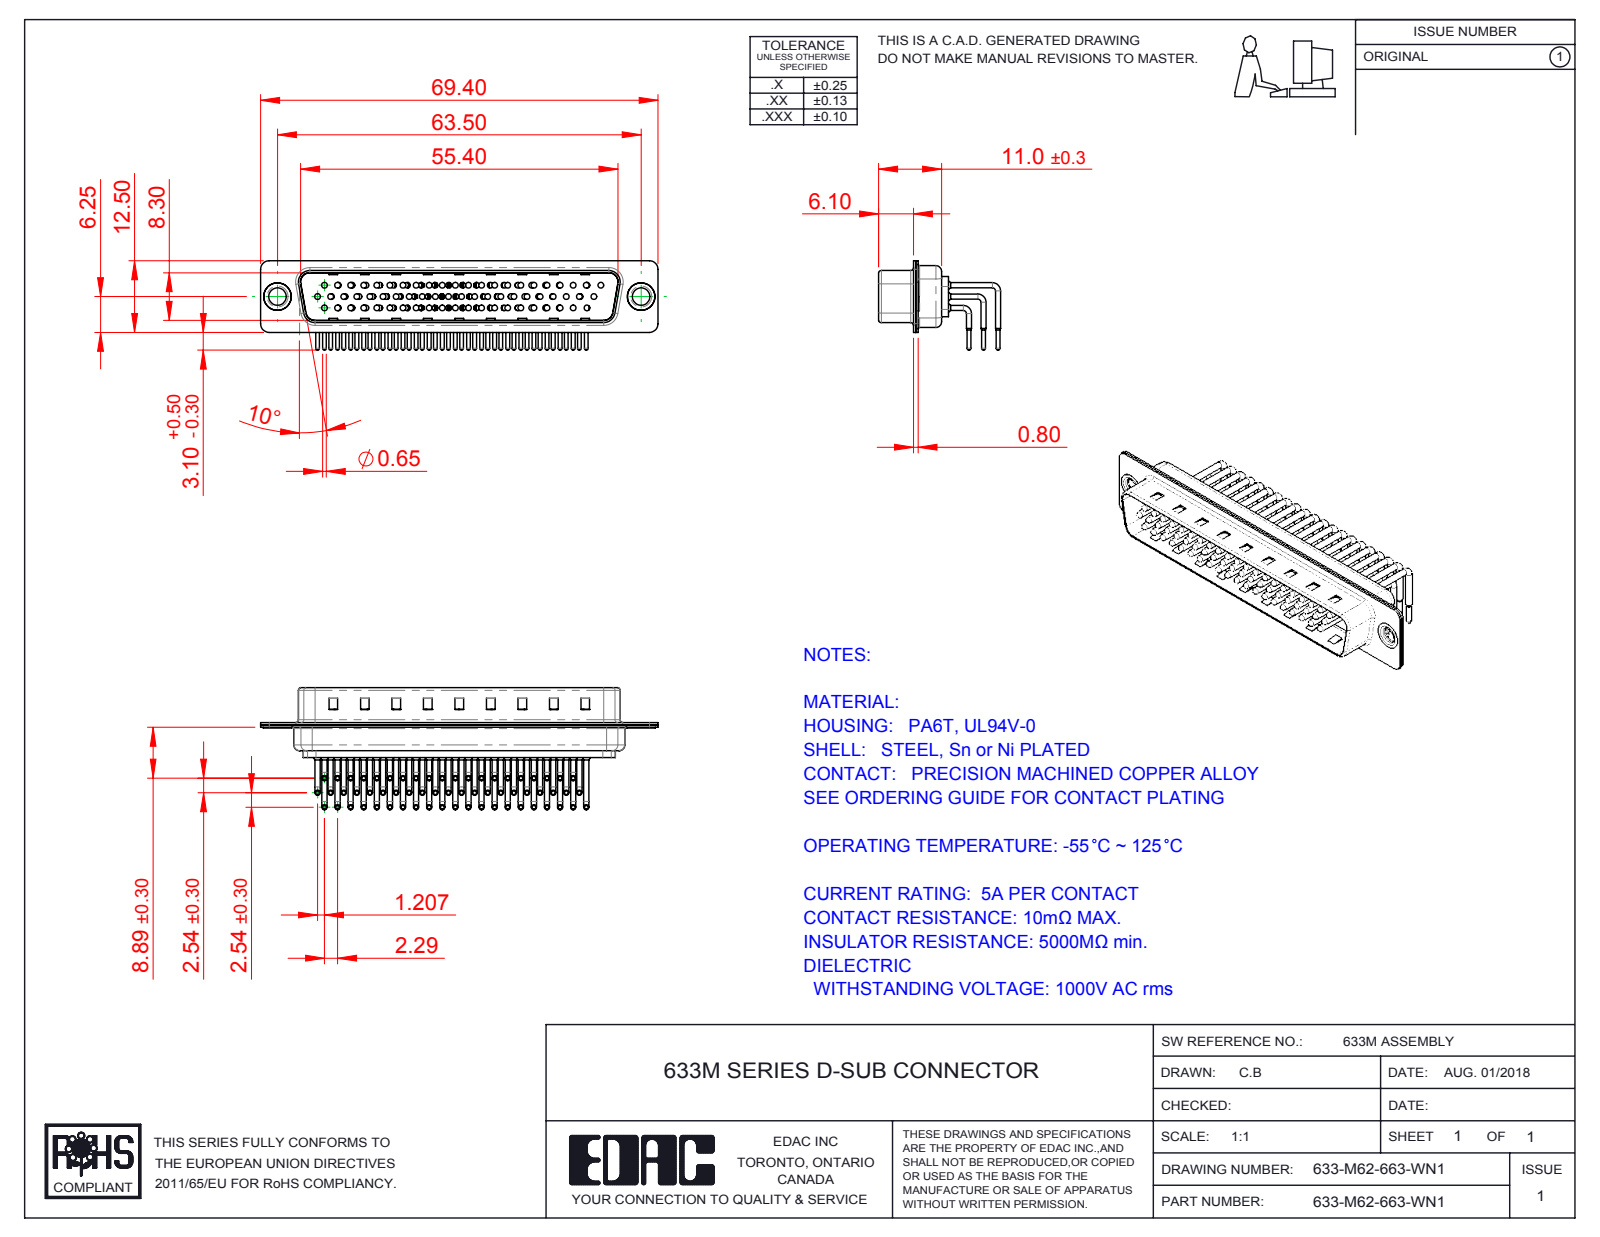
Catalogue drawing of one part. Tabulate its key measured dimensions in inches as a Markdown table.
| quantity | value |
| --- | --- |
| part name | 633M Contact Row 3; 633M Contact Row 2; 633M Shell Front_62 Contacts; 633M Thru Hole Rivet (+4 more) |
| STEP written by | SolidWorks 2016 (CONFIG_CONTROL_DESIGN) |
| units | inches |
| bodies | 67 solids, 7206 faces (4171 planar, 2357 cylindrical, 678 other) |
| overall size | 2.732 × 0.839 × 0.614 |
| volume | 0.261 in³ |
| surface area | 20.92 in² |
| round holes (diameter × count) | 0.039 × 62, 0.067 × 62, 0.079 × 62, 0.12 × 2, 0.157 × 2, 0.189 × 2 |
| round bosses / shafts (diameter × count) | 0.035 × 124, 0.059 × 62, 0.026 × 62, 0.039 × 56, 0.197 × 2, 0.193 × 2, 0.14 × 2 |
| partial cylindrical surfaces (radius × count) | 0.04 × 62, 0.059 × 16, 0.079 × 12, 0.02 × 8, 0.063 × 8, 0.01 × 4, 0.024 × 4, 0.026 × 4 |
| main face-to-face distances | 0.016, 0.033, 0.376, 0.343, 0.059, 0.075, 0.049, 0.409, 0.014, 0.018 |
| hole center spacings | 0.285, 0.091, 0.095, 0.163, 0.38, 0.19, 0.57, 0.435 |
